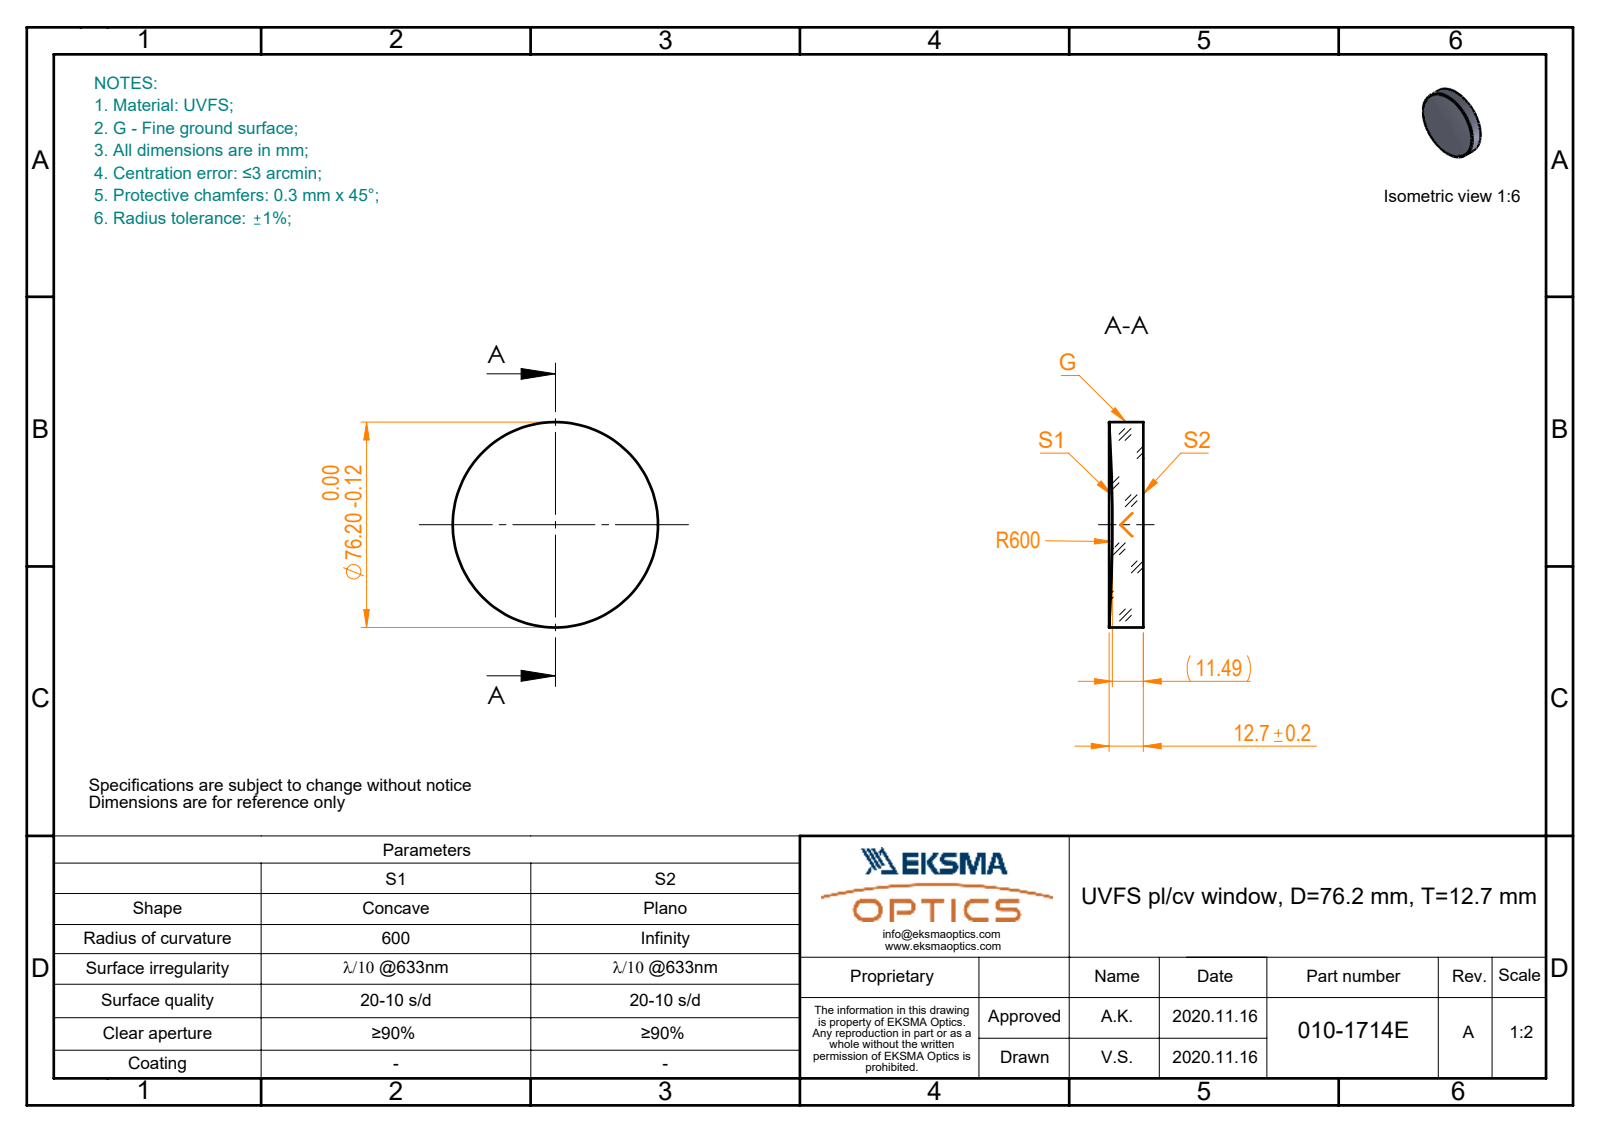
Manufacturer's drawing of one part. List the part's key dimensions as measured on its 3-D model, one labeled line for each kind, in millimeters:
Part name (STEP PRODUCT): 010-1714E_UVFS_PCV_window
STEP written by: SolidWorks 2019 (CONFIG_CONTROL_DESIGN)
Units: millimetres
Bodies: 1 solid, 5 faces (1 planar, 2 cylindrical, 2 other)
Overall size (bounding box): 76.2 × 76.2 × 12.7
Volume: 55 155 mm³ · Surface area: 12 166 mm²
Round bosses / shafts (diameter × count): ⌀76.2 ×1
